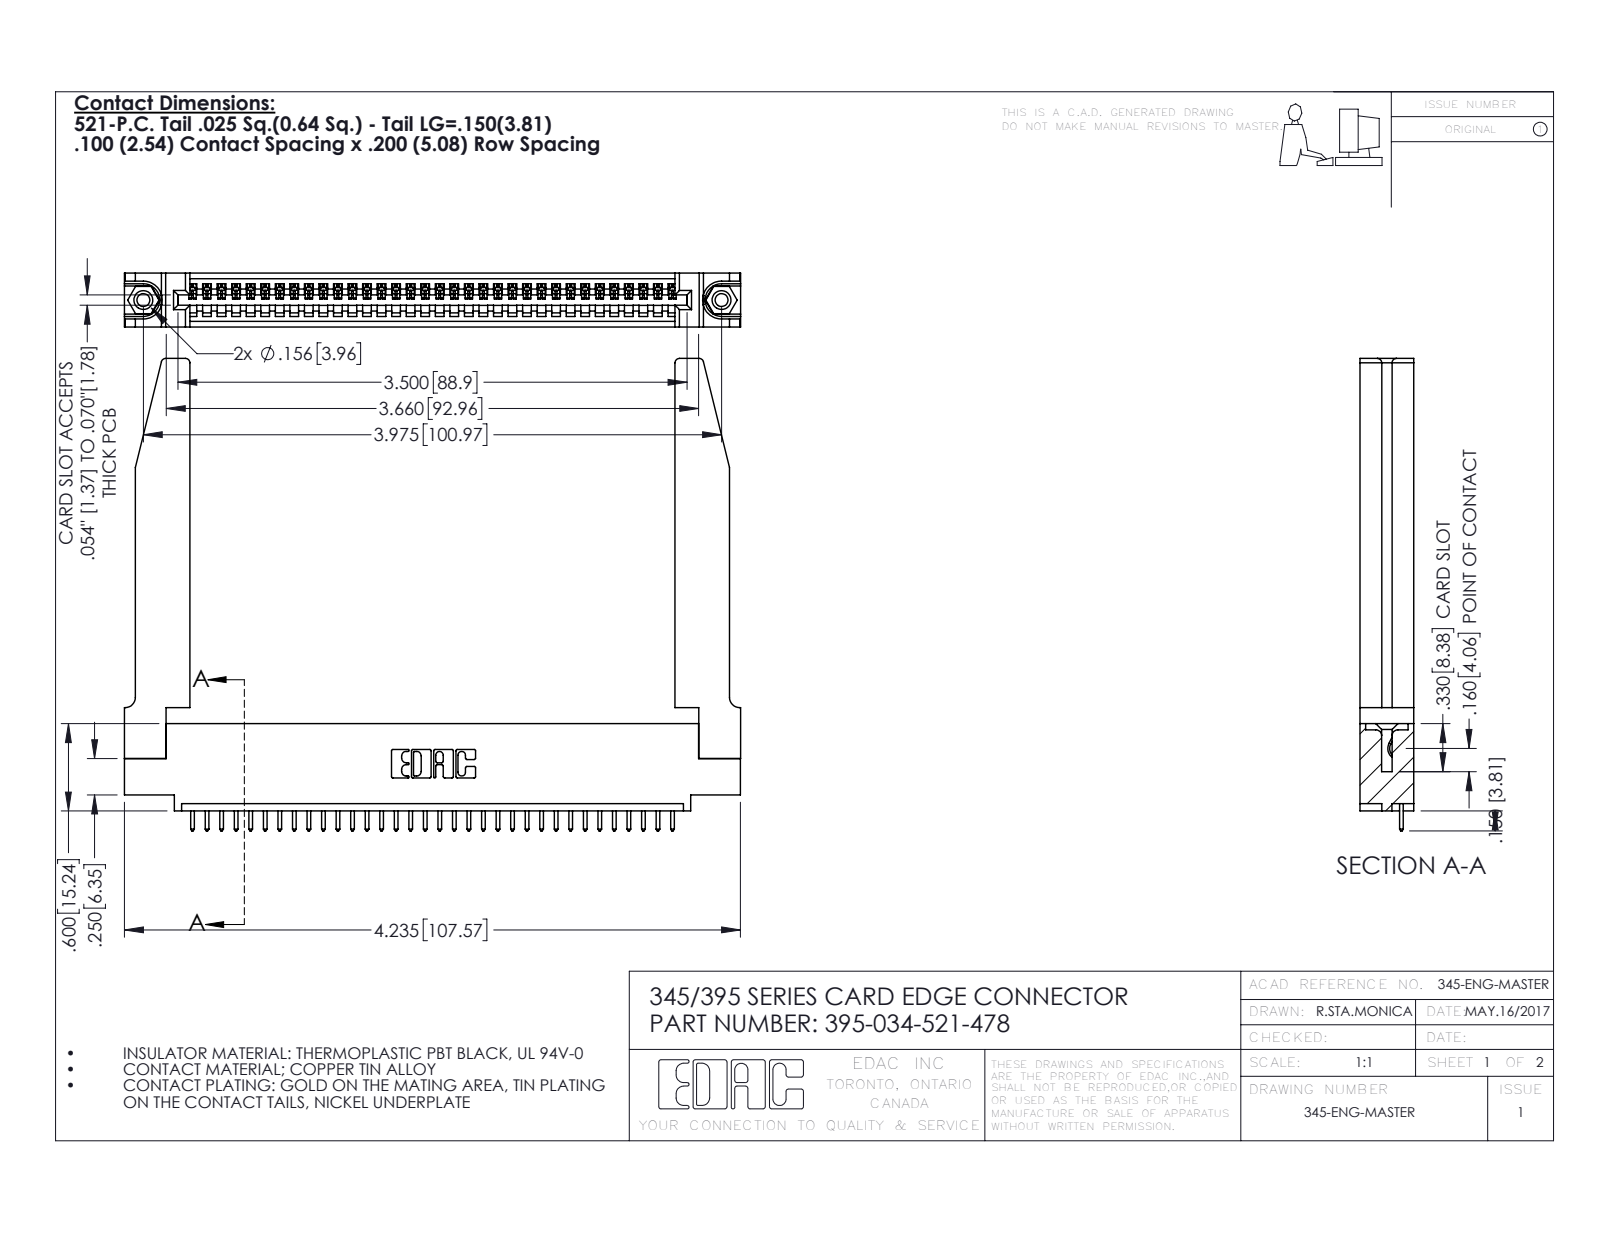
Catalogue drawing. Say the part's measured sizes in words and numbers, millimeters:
The part is named "345-220-078_345-220-078; 345-292-001_345-293-121; 345 Part_0.110 Offset - 0.156 Dia-TH; 345-250-001_345-250-001-102 (+1 more)". Its 3-D file was written by "SolidWorks 2016 (CONFIG_CONTROL_DESIGN)". It is 39 solids with 2336 faces: 1586 planar, 698 cylindrical and 52 other. Overall it measures 107.6 by 82.5 by 9.4 millimeters. Its volume is 17 750 cubic millimeters and its surface area 19 710 square millimeters. Round holes: 2 of diameter 2.3, 2 of diameter 3.2, 2 of diameter 4, 1 of diameter 1.6. Round bosses or shafts: 2 of diameter 3.9. Partial cylindrical surfaces (rounded edges, fillets, slot ends): 68 of radius 0.2, 68 of radius 0.3, 22 of radius 0.3, 8 of radius 0.8, 6 of radius 0.2, 6 of radius 0.8, 3 of radius 0.7, 2 of radius 0.8. The main face-to-face distances are 9.4, 1.8, 7.6, 5.1, 2.5, 6.9, 0.6, 5.7, 3.8, 3.8. The hole center spacings are 6.9, 95, 101.
